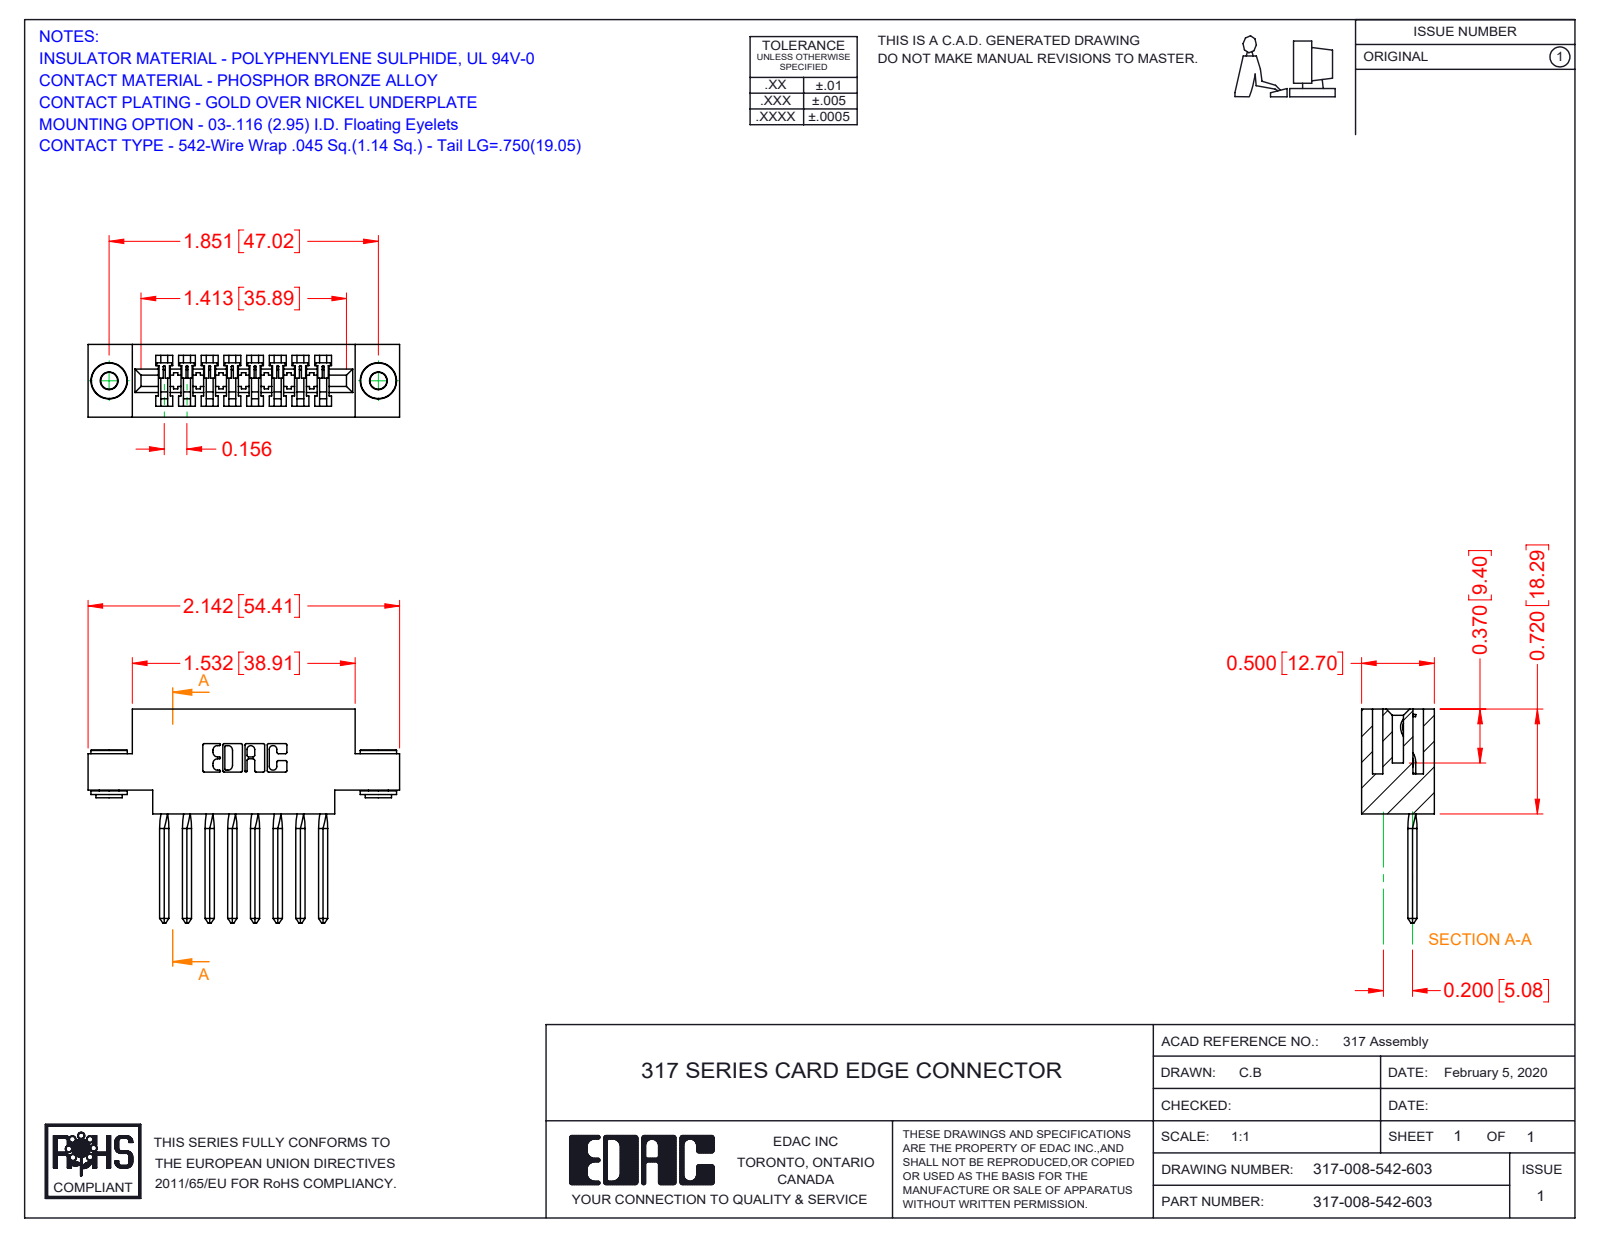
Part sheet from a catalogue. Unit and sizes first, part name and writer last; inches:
Units: inches
Overall size (bounding box): 2.142 × 1.47 × 0.5
Round holes (diameter × count): ⌀0.116 ×2, ⌀0.156 ×2
Round bosses / shafts (diameter × count): ⌀0.25 ×2, ⌀0.18 ×2, ⌀0.136 ×2
Partial cylindrical surfaces — rounded edges, fillets, slot ends (radius × count): R0.01 ×22, R0.006 ×16, R0.007 ×6, R0.031 ×6, R0.026 ×3, R0.074 ×1, R0.089 ×1, R0.1 ×1
Main face-to-face distances: 0.5, 0.075, 0.425, 0.11, 0.065, 0.22, 0.156, 0.116, 0.35, 0.305
Hole centre spacings: 1.851
Volume: 0.459 in³ · Surface area: 13.38 in²
Bodies: 11 solids, 740 faces (580 planar, 120 cylindrical, 40 other)
Part name (STEP PRODUCT): 317-290-003_542; 317 Part_.156 Dia - TH; 317-008-542-603; 345-250-002_345-250-002-102
STEP written by: SolidWorks 2016 (CONFIG_CONTROL_DESIGN)
